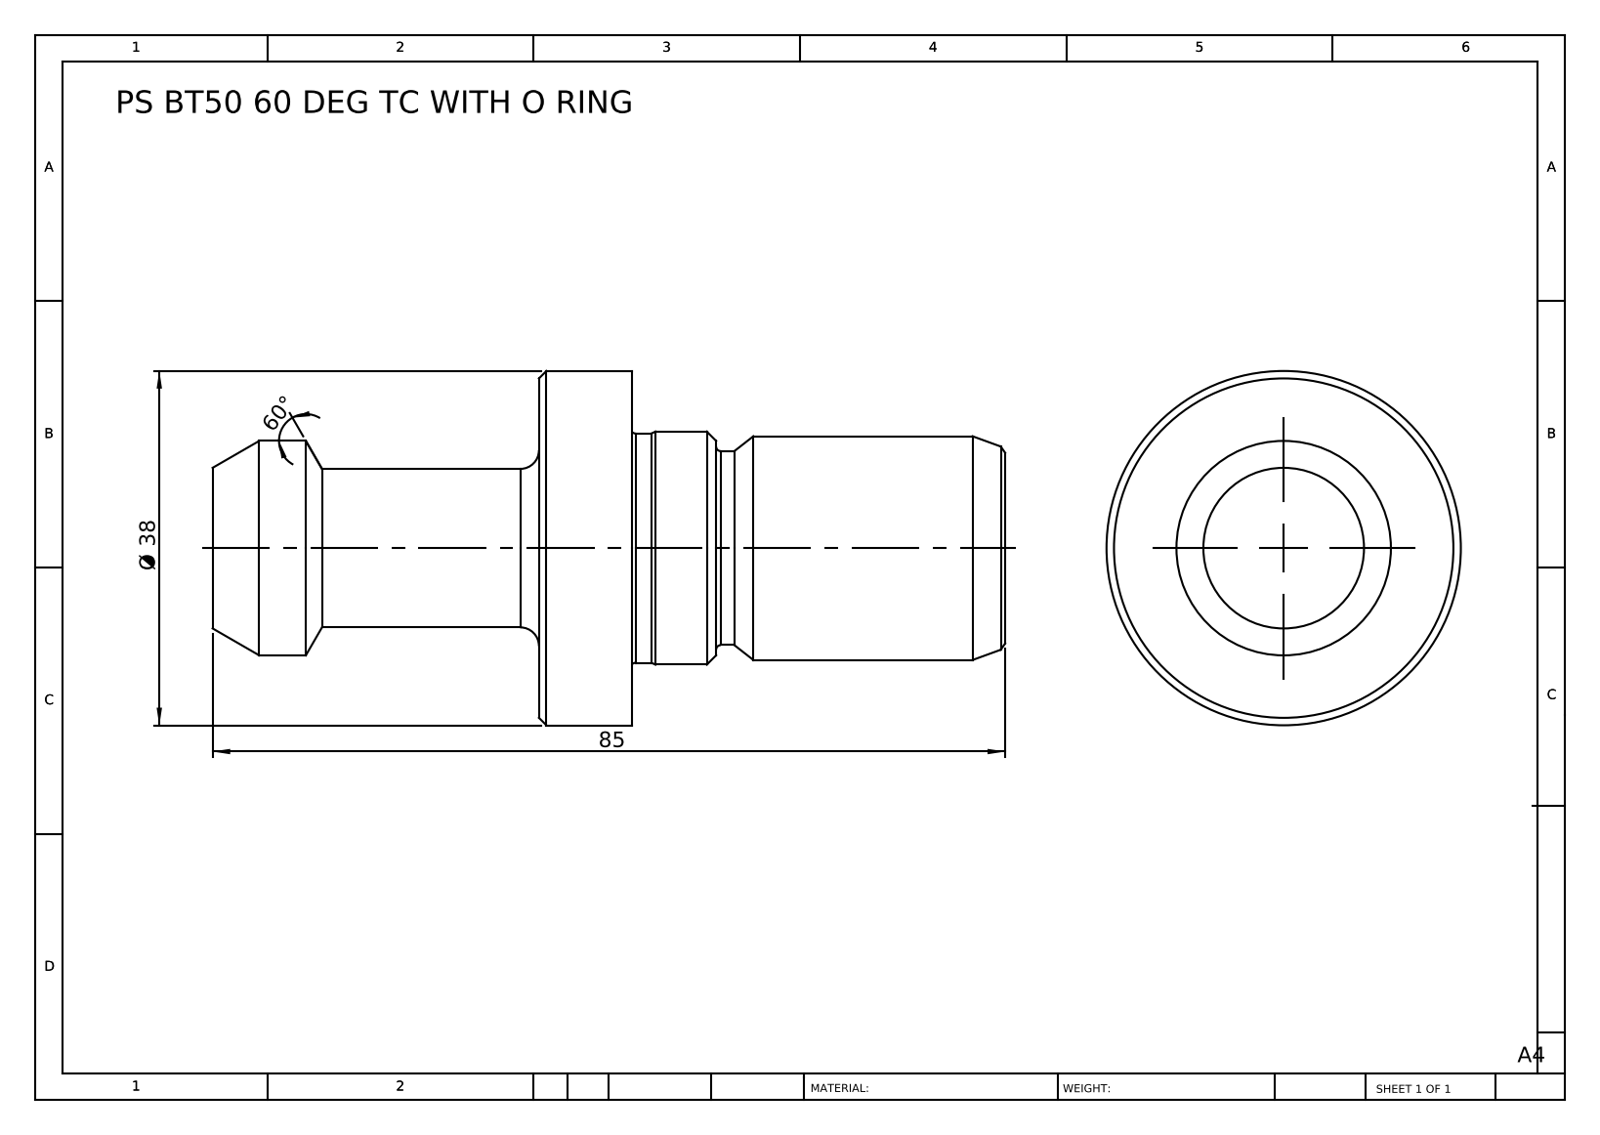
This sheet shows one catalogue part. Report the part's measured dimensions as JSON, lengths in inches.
{"part_name": "PS BT50 60 DEG TC WITH O RING", "step_written_by": "SolidWorks 2014 (CONFIG_CONTROL_DESIGN)", "units": "inches", "bodies": {"solids": 1, "faces": 43, "planar": 5, "cylindrical": 14, "other": 24}, "overall_size": [3.346, 1.496, 1.496], "volume_in3": 2.363, "surface_area_in2": 13.28, "round_bosses_or_shafts": [[1.496, 1], [0.984, 1], [0.969, 1], [0.945, 1], [0.906, 1], [0.819, 1], [0.669, 1]], "face_to_face_distances": [0.394, 1.575, 1.969, 3.346, 1.772, 1.378, 1.22, 0.354, 0.748, 2.126]}
